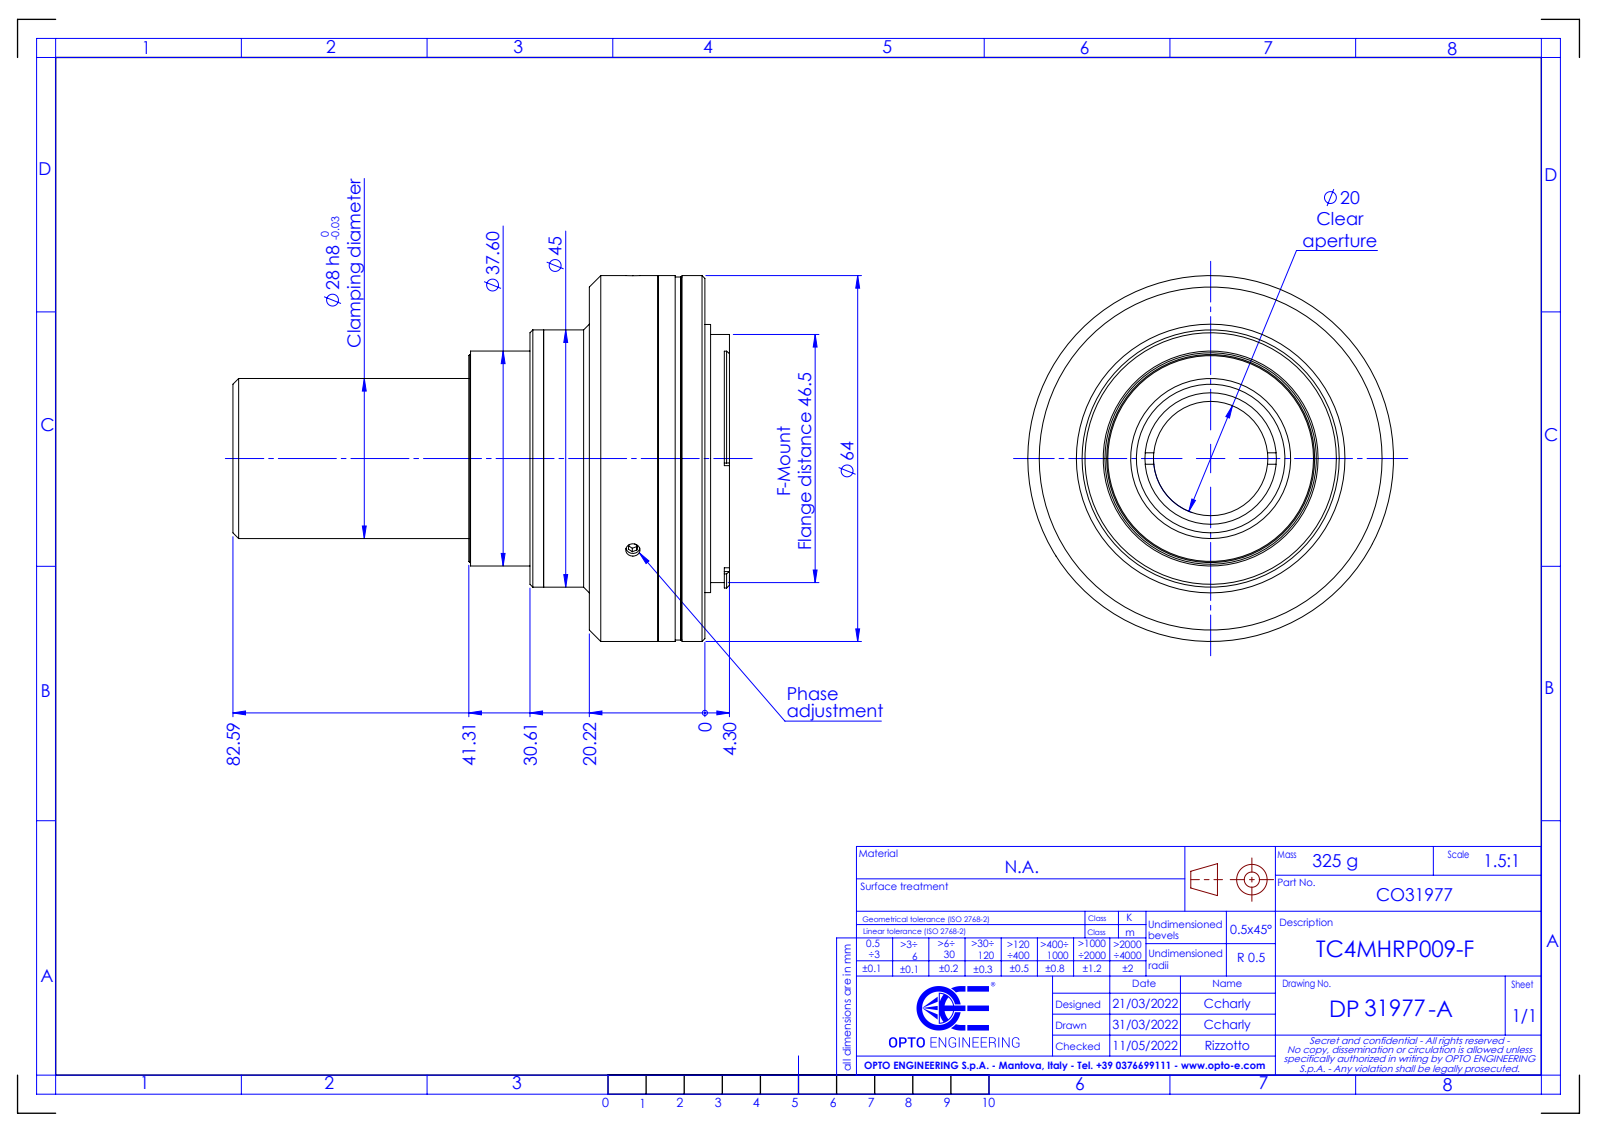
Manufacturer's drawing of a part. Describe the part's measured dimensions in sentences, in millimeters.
The part is named "DP31977-A_TC4MHRP009-F". Its 3-D file was written by "SolidWorks 2021 (CONFIG_CONTROL_DESIGN)". It is 0 solids with 148 faces: 62 planar, 53 cylindrical and 33 other. Overall it measures 86.89 by 64 by 64 millimeters. Round holes: 3 of diameter 2.5, 1 of diameter 18, 1 of diameter 20, 1 of diameter 21.5, 1 of diameter 23, 1 of diameter 42. Round bosses or shafts: 1 of diameter 64, 1 of diameter 63.5, 1 of diameter 46.9, 1 of diameter 45, 1 of diameter 43.4, 1 of diameter 37.6, 1 of diameter 36.4, 1 of diameter 28. Partial cylindrical surfaces (rounded edges, fillets, slot ends): 6 of radius 0.5, 2 of radius 1.15, 1 of radius 22.65. The main face-to-face distances are 18.72, 10.52, 8.2, 1.5, 13.52, 3, 5.2, 12.02, 15.02, 20.22.
